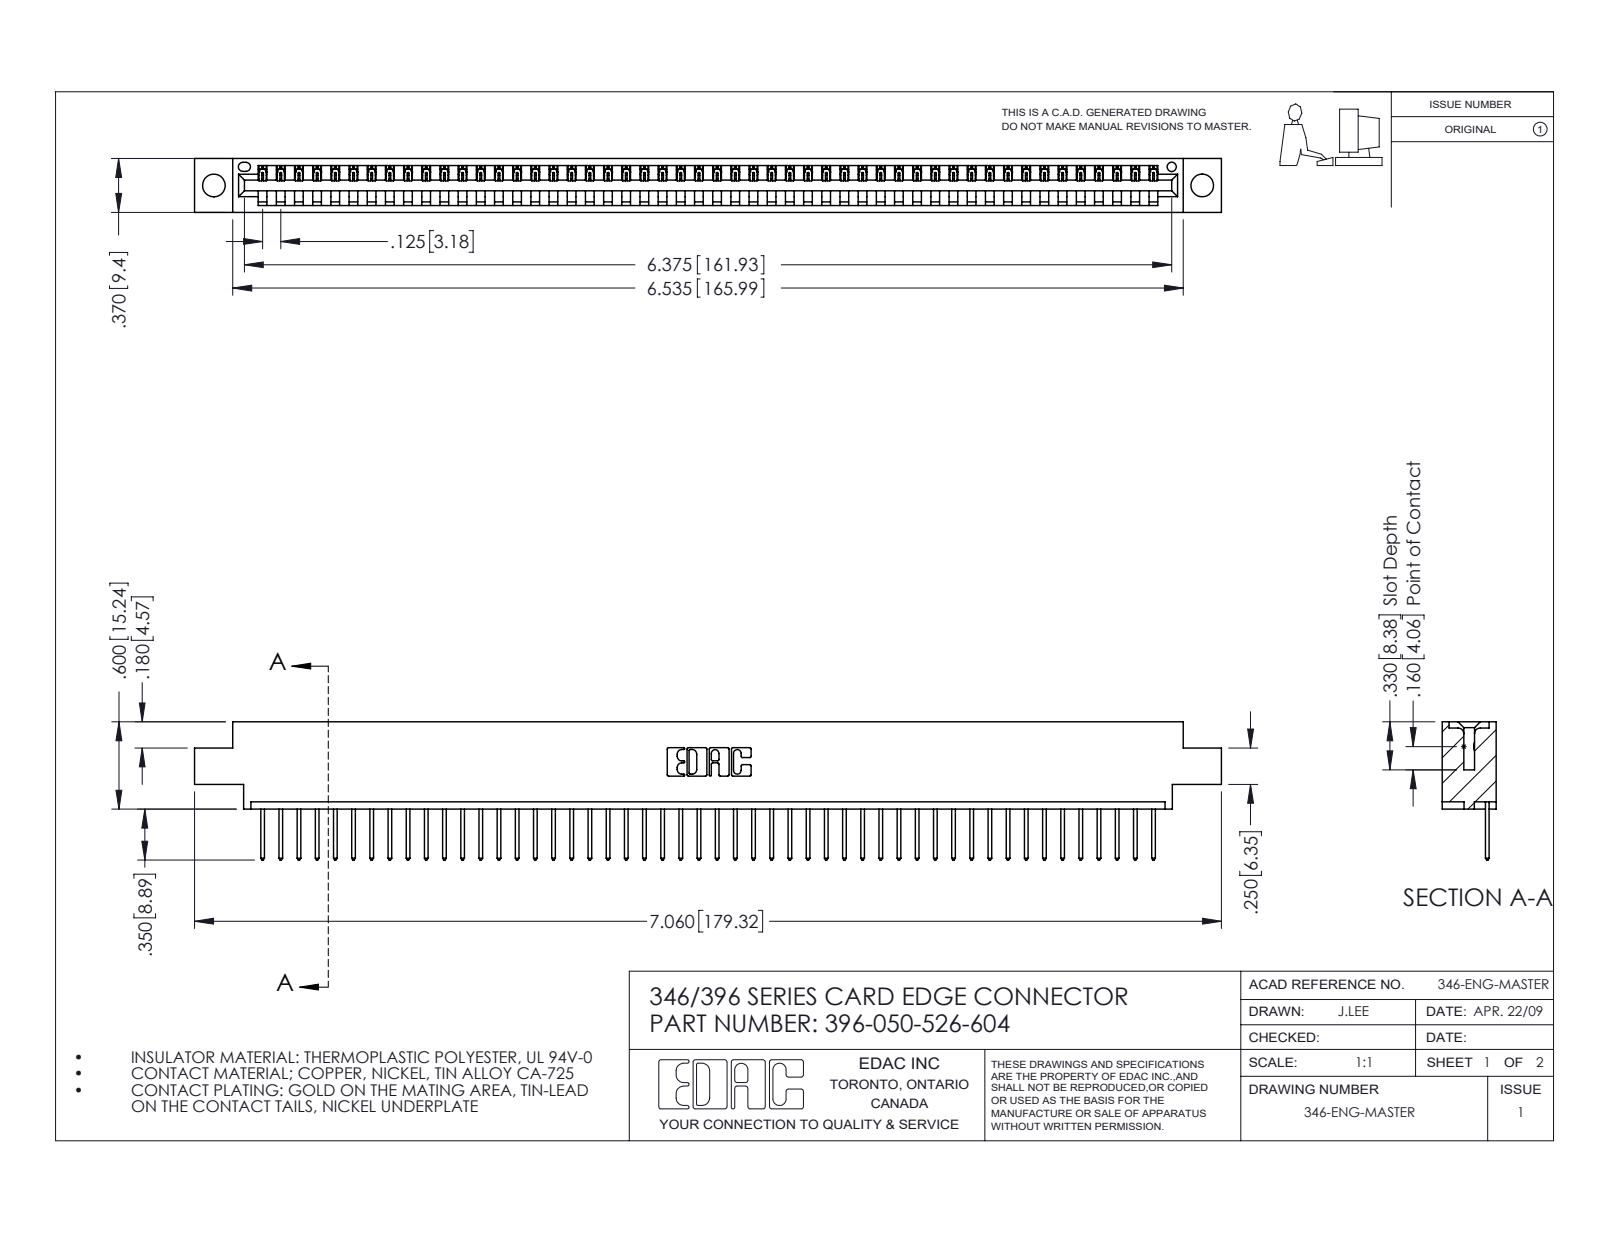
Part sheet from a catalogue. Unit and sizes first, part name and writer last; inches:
Units: inches
Overall size (bounding box): 7.06 × 0.95 × 0.37
Round holes (diameter × count): ⌀0.156 ×2, ⌀0.064 ×1
Partial cylindrical surfaces — rounded edges, fillets, slot ends (radius × count): R0.006 ×100, R0.01 ×100, R0.01 ×22, R0.007 ×6, R0.031 ×6, R0.026 ×3, R0.031 ×2, R0.04 ×2
Main face-to-face distances: 0.048, 0.322, 0.37, 0.25, 0.072, 0.298, 0.025, 0.148, 0.222, 0.1
Hole centre spacings: 0.246, 6.586, 6.795
Volume: 1.034 in³ · Surface area: 32.82 in²
Bodies: 51 solids, 3026 faces (2080 planar, 946 cylindrical, 0 other)
Part name (STEP PRODUCT): 345-292-001_345-293-126; 396-050-526-604; 346 Part_0.170 Offset - 0.156 Dia-TH
STEP written by: SolidWorks 2016 (CONFIG_CONTROL_DESIGN)
